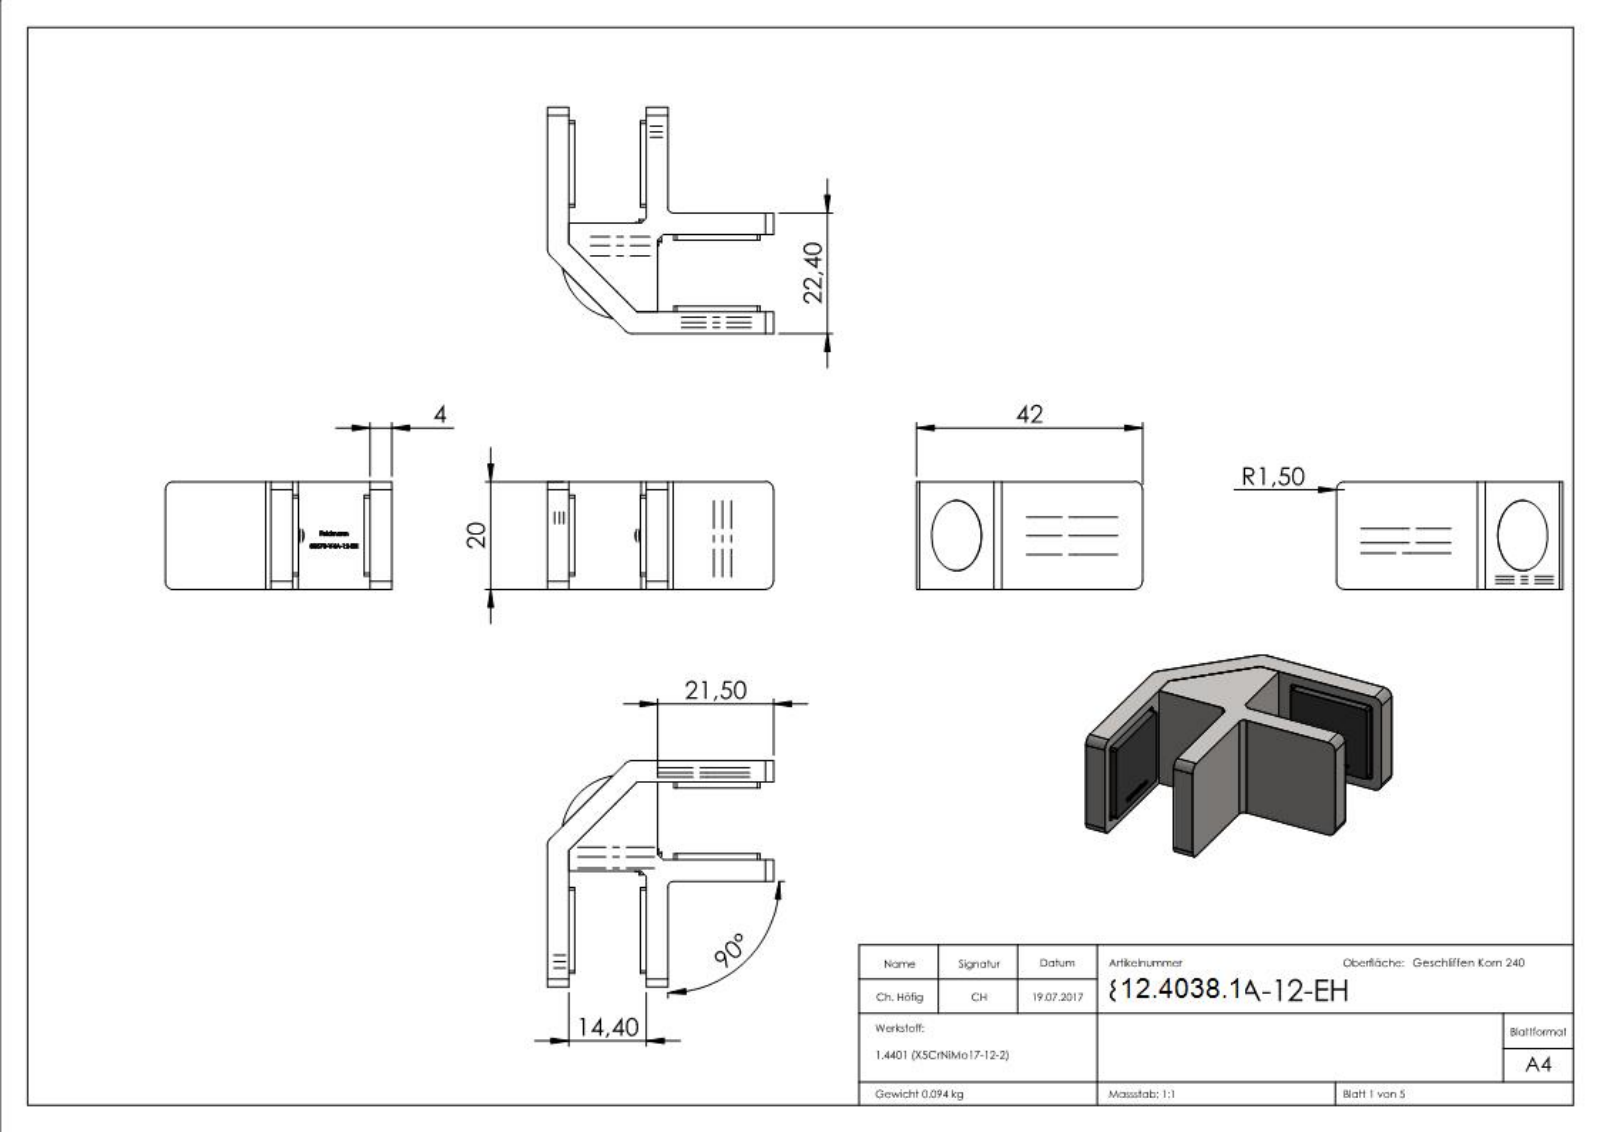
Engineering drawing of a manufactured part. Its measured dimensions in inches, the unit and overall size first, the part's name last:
Units: inches
Overall size (bounding box): 1.654 × 1.654 × 0.787
Round holes (diameter × count): ⌀0.106 ×2, ⌀0.071 ×1, ⌀0.197 ×1, ⌀0.276 ×1, ⌀0.492 ×1
Round bosses / shafts (diameter × count): ⌀0.456 ×1, ⌀0.236 ×1, ⌀0.157 ×1
Partial cylindrical surfaces — rounded edges, fillets, slot ends (radius × count): R0.008 ×56, R0.02 ×48, R0.059 ×4, R0.079 ×2, R0.039 ×1
Main face-to-face distances: 0.138, 0.063, 0.157, 0.744, 0.02, 0.606, 0.724, 0.201, 0.681, 0.543
Hole centre spacings: 0.323, 0.646
Volume: 0.845 in³ · Surface area: 17.48 in²
Bodies: 8 solids, 2904 faces (1621 planar, 209 cylindrical, 1074 other)
Part name (STEP PRODUCT): socket countersunk head screw_din; 80570-V4A-12-EH; 80570-xxx-xx-EH Teil3; 80570-xxx-xx-EH Teil2 (+6 more)
STEP written by: SolidWorks 2018 (CONFIG_CONTROL_DESIGN)
